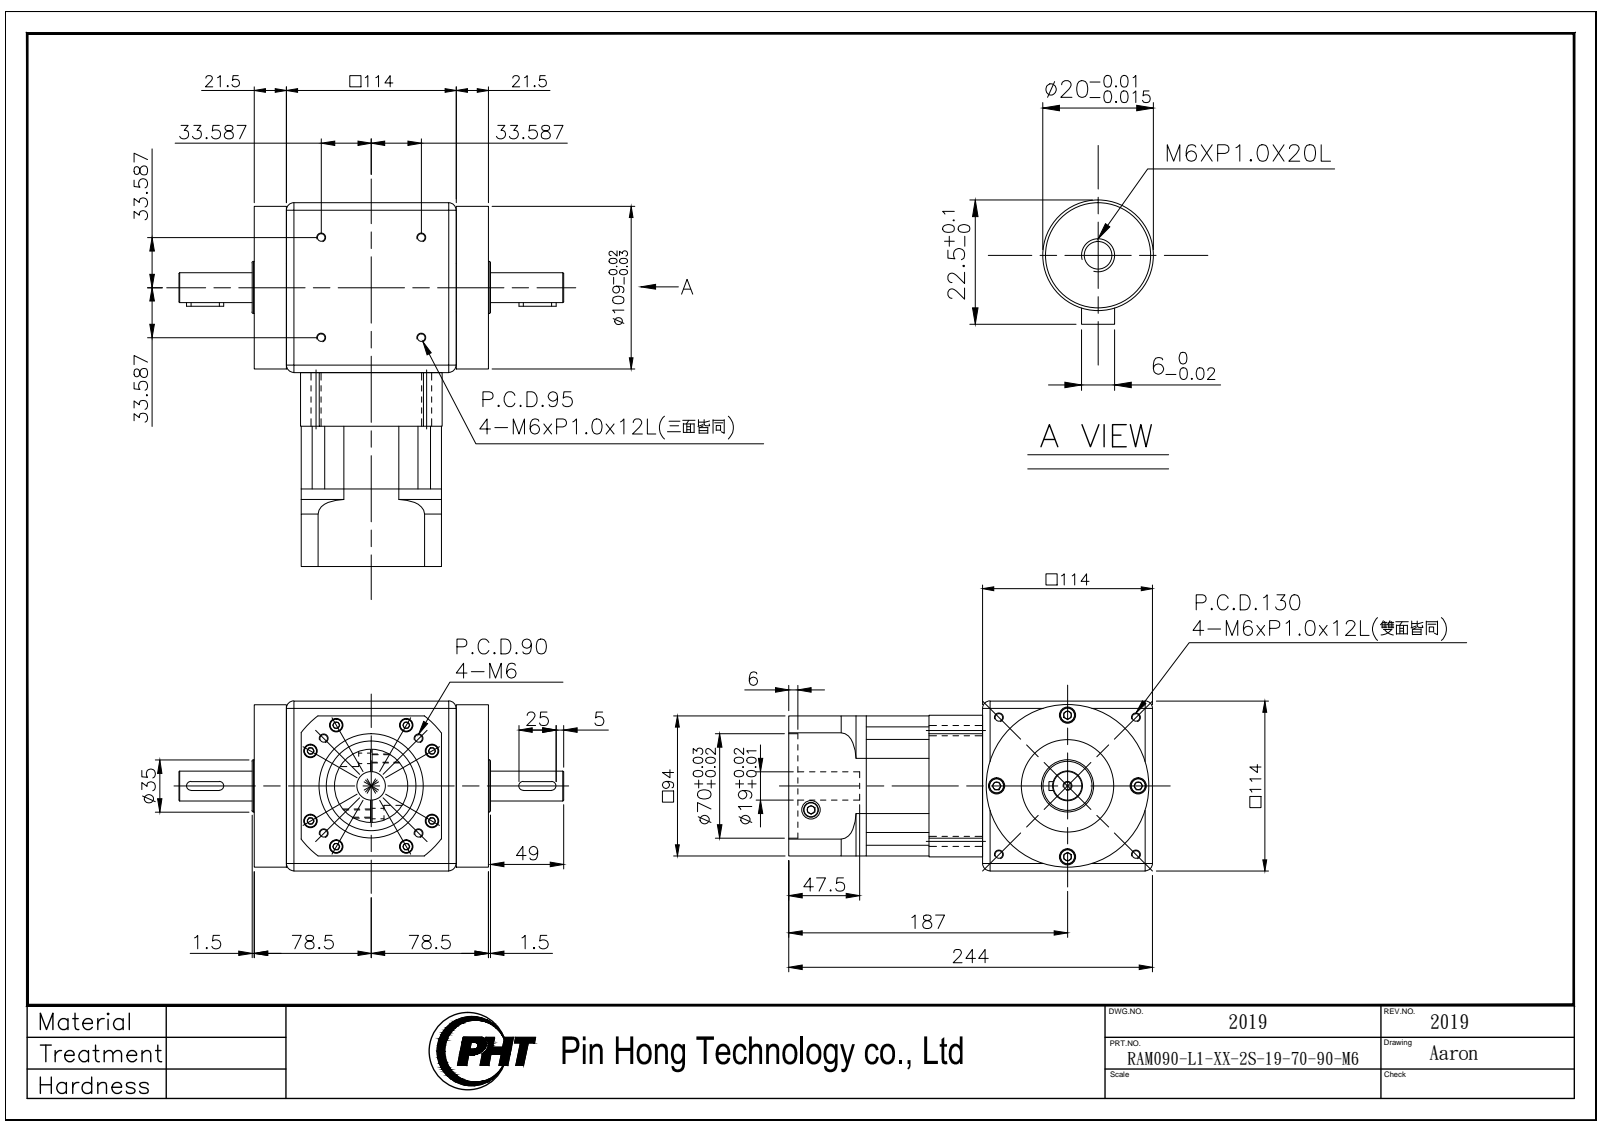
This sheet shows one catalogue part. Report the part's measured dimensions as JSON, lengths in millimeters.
{"part_name": "RAM090-L1-XX-2S-19-70-90-M6_2019", "step_written_by": "SolidWorks 2016 (AUTOMOTIVE_DESIGN)", "units": "millimeters", "bodies": {"solids": 3, "faces": 672, "planar": 300, "cylindrical": 236, "other": 136}, "overall_size": [258, 244, 114], "volume_mm3": 2871000, "surface_area_mm2": 227548, "round_holes": [[5, 17], [5.2, 8], [9, 8], [6.6, 4], [6.8, 4], [11, 4], [12.7, 2], [2.5, 1], [19, 1], [60, 1], [70, 1]], "round_bosses_or_shafts": [[10, 8], [8.5, 8], [109, 1], [80, 1], [62, 1], [49, 1], [35, 1], [20, 1]], "partial_cylinders_radius": [[3, 4], [6, 4], [50.5, 1], [59, 1], [79.1, 1]], "face_to_face_distances": [114, 10, 104, 78, 192, 94, 104.5, 9.5, 0.5, 94.5], "hole_center_spacings": [47, 67.18, 12.17, 12.34, 14.08, 45.99, 47.5, 56.03]}
